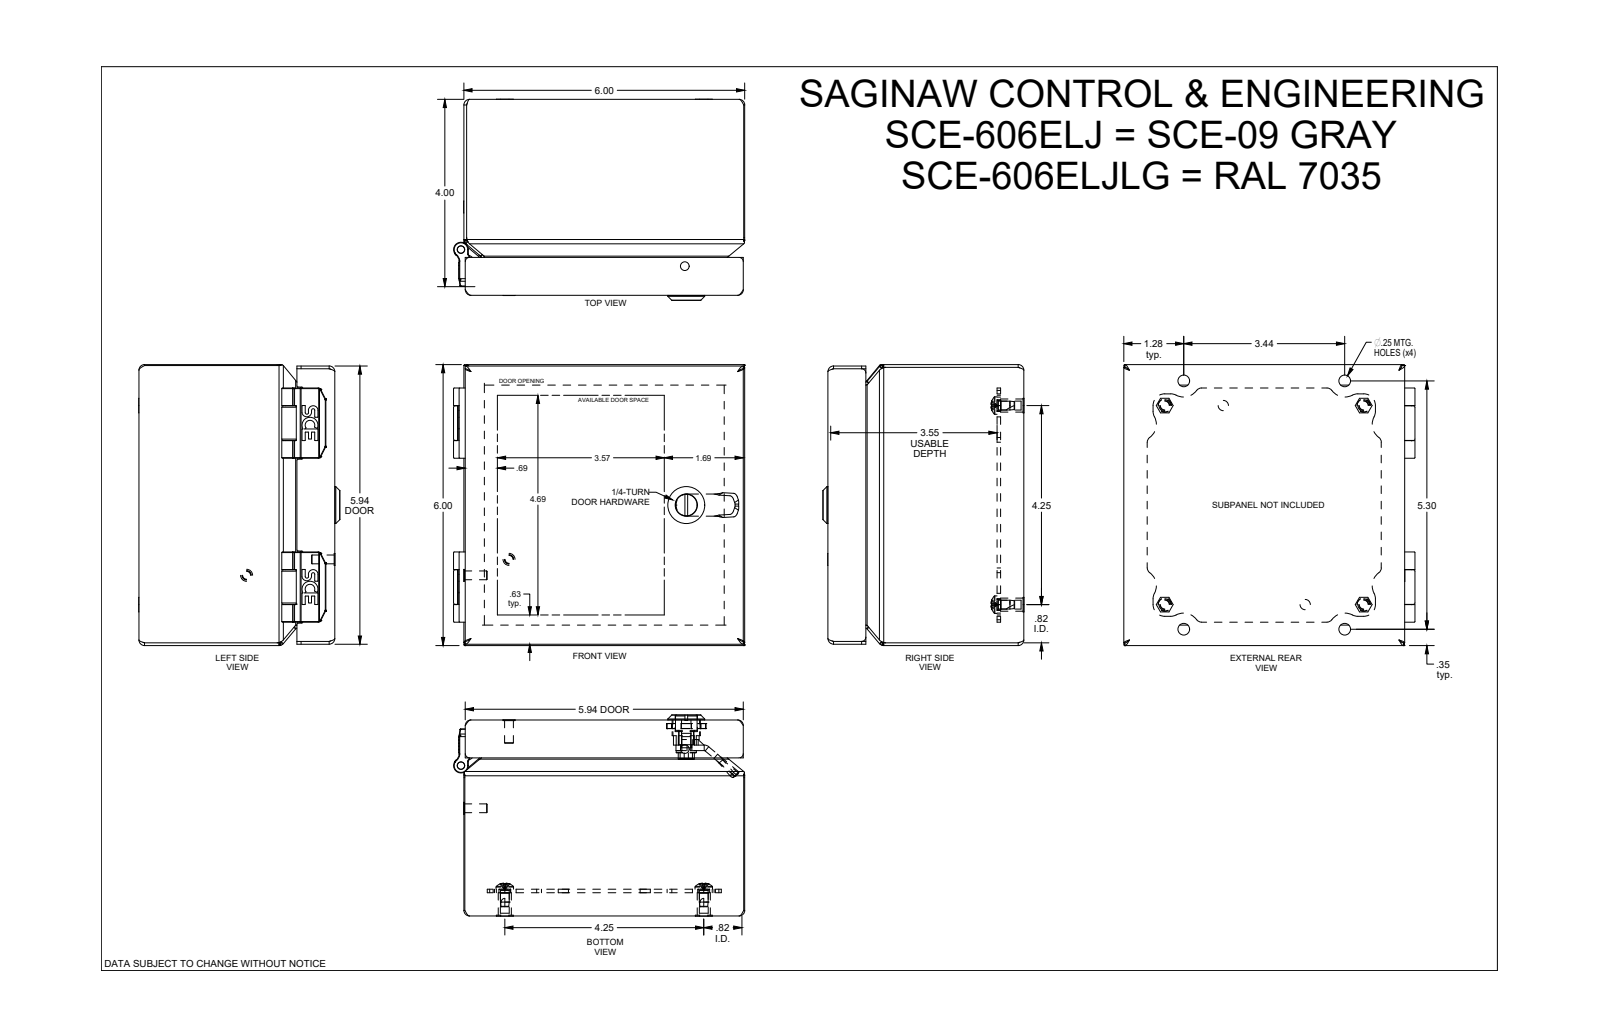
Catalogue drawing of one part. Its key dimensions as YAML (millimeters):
part_name: "SCE-606ELJ"
step_written_by: "SolidWorks 2021 (AUTOMOTIVE_DESIGN)"
units: millimeters
bodies: {solids: 22, faces: 1294, planar: 401, cylindrical: 390, other: 503}
overall_size: [158, 152.4, 109]
volume: 221600
surface_area: 281900
round_holes:
  - {diameter: 6.4, count: 8}
  - {diameter: 7.2, count: 4}
  - {diameter: 4.3, count: 2}
  - {diameter: 5.5, count: 2}
  - {diameter: 4, count: 1}
  - {diameter: 5.1, count: 1}
  - {diameter: 6.1, count: 1}
  - {diameter: 6.5, count: 1}
  - {diameter: 6.8, count: 1}
  - {diameter: 7.2, count: 1}
  - {diameter: 8.3, count: 1}
  - {diameter: 12.1, count: 1}
round_bosses_or_shafts:
  - {diameter: 4.8, count: 5}
  - {diameter: 9.5, count: 4}
  - {diameter: 7.2, count: 4}
  - {diameter: 12.2, count: 2}
  - {diameter: 6.6, count: 2}
  - {diameter: 2.5, count: 2}
  - {diameter: 0.5, count: 2}
  - {diameter: 20, count: 1}
partial_cylinders:
  - {radius: 2.7, count: 66}
  - {radius: 0.1, count: 36}
  - {radius: 0.2, count: 32}
  - {radius: 0.3, count: 21}
  - {radius: 1.3, count: 16}
  - {radius: 0.6, count: 12}
  - {radius: 6.4, count: 12}
  - {radius: 0.3, count: 10}
face_to_face_distances: [1.5, 150.9, 1.6, 152.4, 149.4, 104.7, 106.3, 104.8, 103.2, 14.5]
hole_center_spacings: [16.9, 98.6, 108, 108, 121.7, 155.7, 16.8, 25.2]
